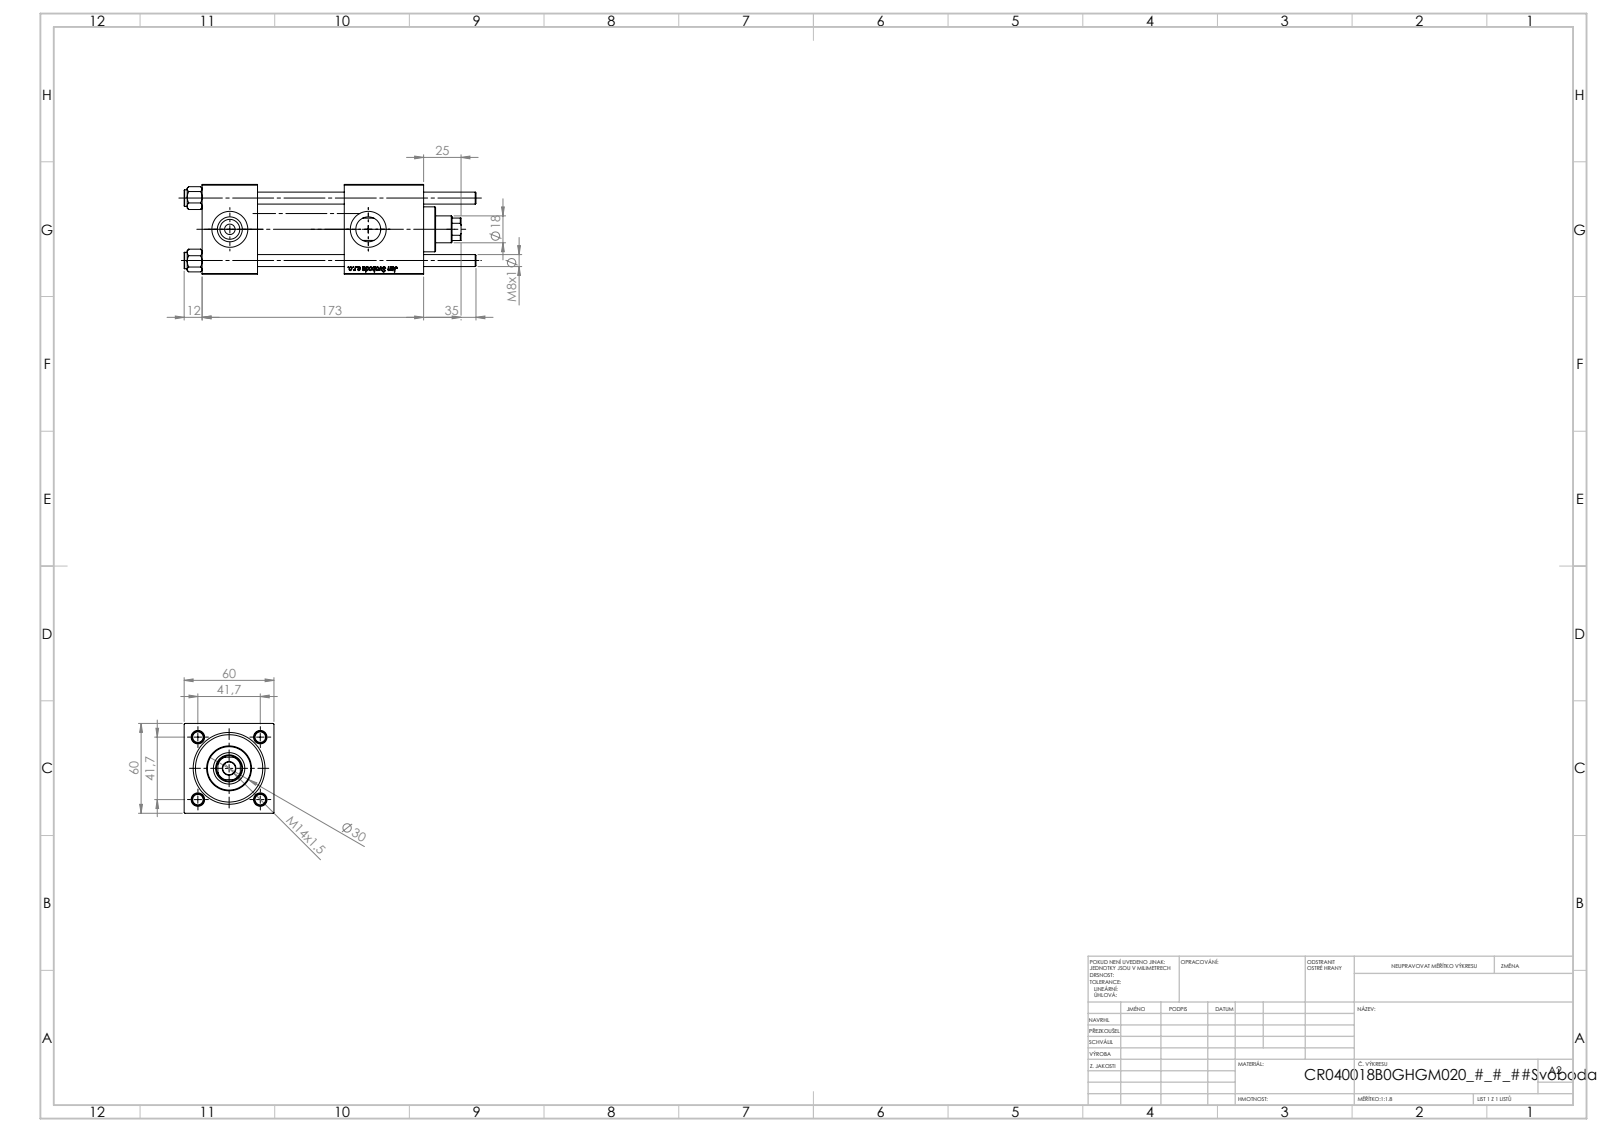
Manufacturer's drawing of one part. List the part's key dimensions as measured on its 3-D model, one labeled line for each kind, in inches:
Part name (STEP PRODUCT): V215_VC_A; V215CR_B-1; V215CR_B_TYCINKA; NUT_M5_B (+1 more)
STEP written by: SolidWorks 2019 (CONFIG_CONTROL_DESIGN)
Units: inches
Bodies: 11 solids, 1159 faces (433 planar, 78 cylindrical, 648 other)
Overall size (bounding box): 7.677 × 2.362 × 2.362
Volume: 25.26 in³ · Surface area: 176.3 in²
Round holes (diameter × count): ⌀0.315 ×4, ⌀0.276 ×2, ⌀0.656 ×2, ⌀0.945 ×2, ⌀0.335 ×1, ⌀0.709 ×1, ⌀0.827 ×1, ⌀1.22 ×1, ⌀1.575 ×1, ⌀1.772 ×1
Round bosses / shafts (diameter × count): ⌀0.433 ×4, ⌀1.811 ×1, ⌀1.181 ×1
Partial cylindrical surfaces — rounded edges, fillets, slot ends (radius × count): R0.335 ×1
Main face-to-face distances: 2.362, 1.457, 5.827, 4.37, 2.283, 2.087, 3.74, 4.697, 3.24, 0.957
Hole centre spacings: 1.161, 1.642, 2.322, 3.642
